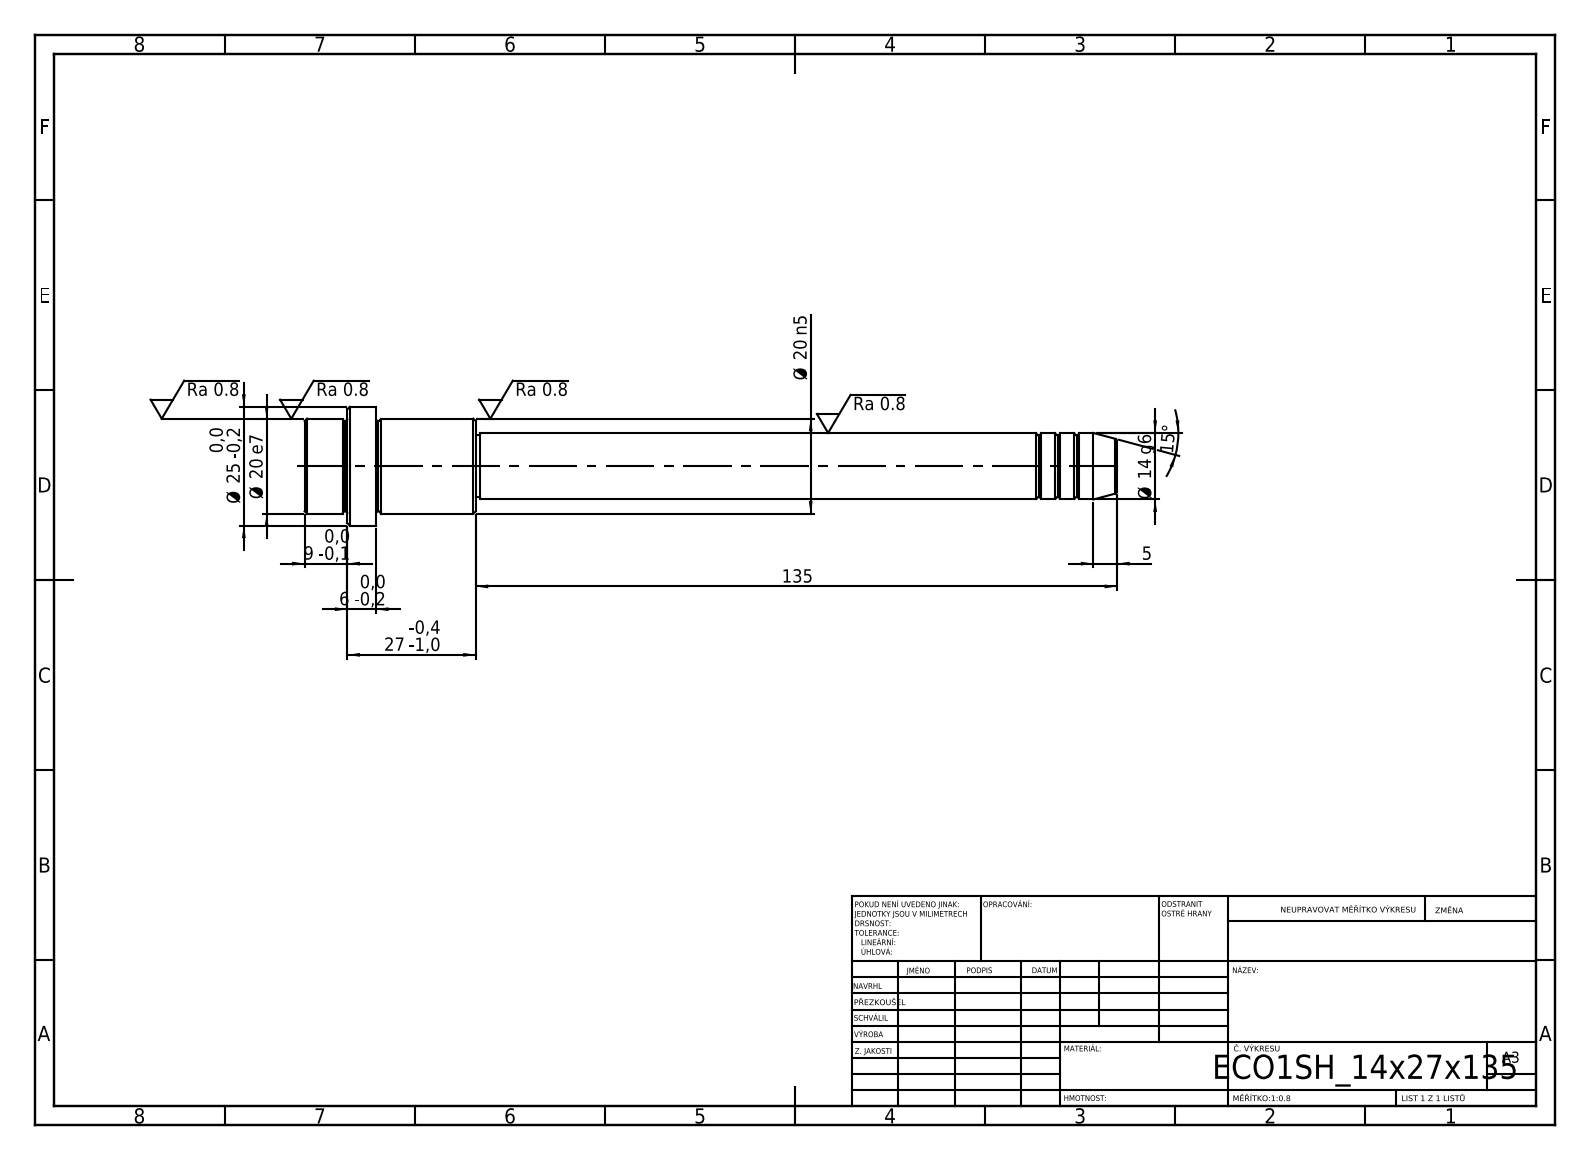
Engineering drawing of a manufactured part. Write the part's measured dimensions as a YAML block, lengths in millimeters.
step_written_by: "SolidWorks 2019 (CONFIG_CONTROL_DESIGN)"
units: millimeters
bodies: {solids: 1, faces: 52, planar: 6, cylindrical: 16, other: 30}
overall_size: [171, 25, 25]
volume: 32868
surface_area: 9314
round_bosses_or_shafts:
  - {diameter: 25, count: 1}
  - {diameter: 20, count: 1}
  - {diameter: 14, count: 1}
  - {diameter: 13, count: 1}
face_to_face_distances: [15, 21, 36, 27, 6, 9, 135, 156, 162, 171]
